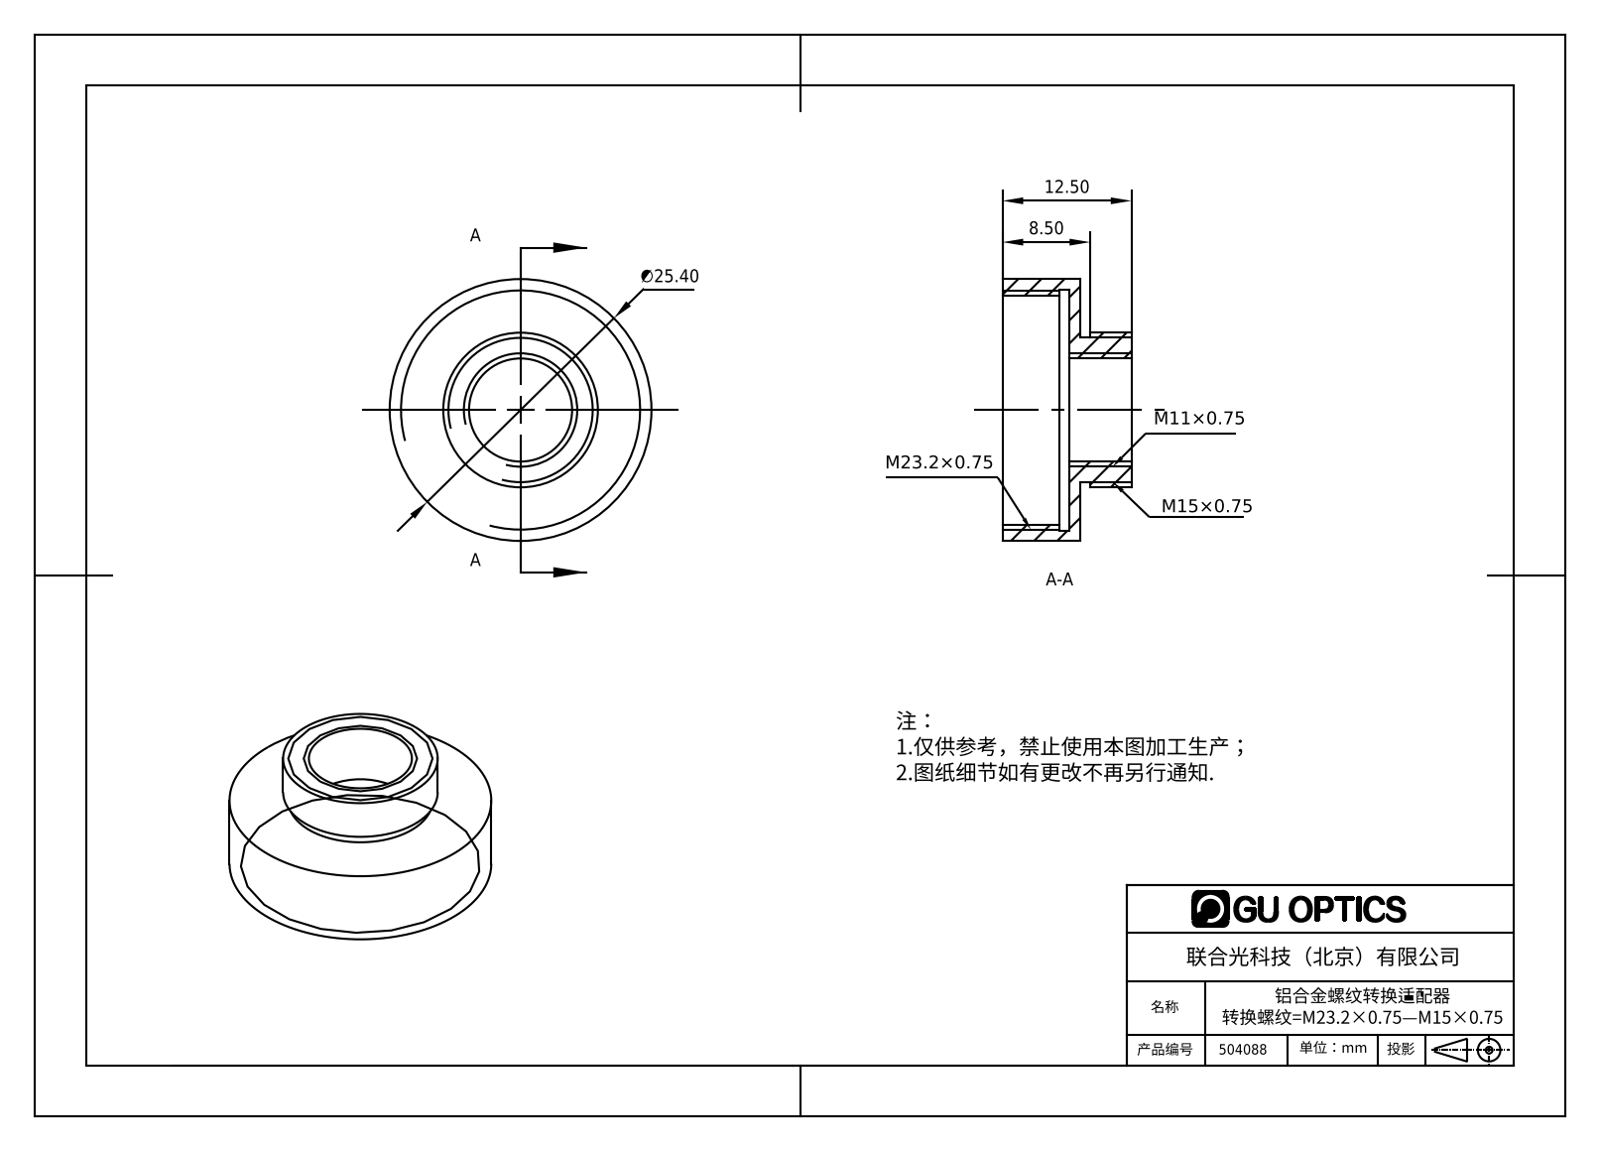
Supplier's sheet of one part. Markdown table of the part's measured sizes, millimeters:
| quantity | value |
| --- | --- |
| part name | 504088 |
| STEP written by | SolidWorks 2016 (AUTOMOTIVE_DESIGN) |
| units | millimeters |
| bodies | 1 solid, 18 faces (6 planar, 12 cylindrical, 0 other) |
| overall size | 25.4 × 25.4 × 12.5 |
| volume | 1 631 mm³ |
| surface area | 2 464 mm² |
| round holes (diameter × count) | 10 × 1, 22.2 × 1, 23.4 × 1 |
| round bosses / shafts (diameter × count) | 25.4 × 1, 15 × 1, 14 × 1 |
| main face-to-face distances | 1, 6.5, 7.5, 12.5, 6, 5, 2, 5.5, 7, 8.5 |
